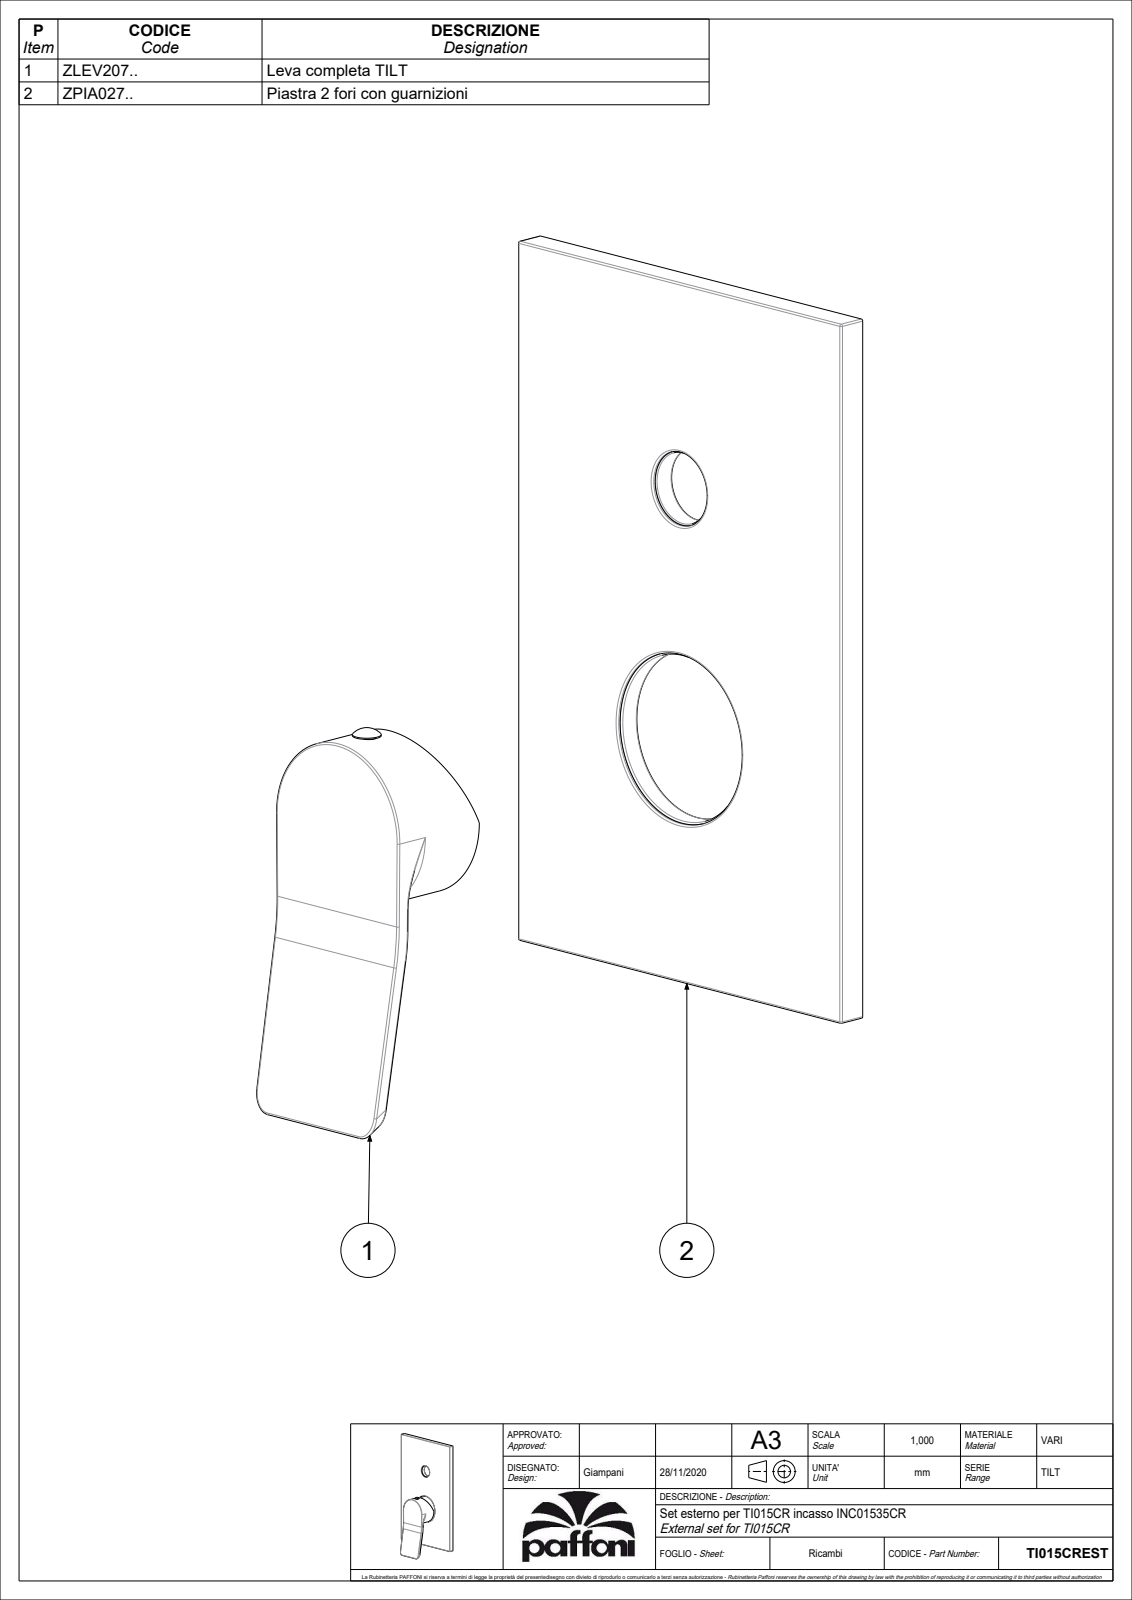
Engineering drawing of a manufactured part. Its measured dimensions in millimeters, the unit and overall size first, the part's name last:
Units: millimetres
Overall size (bounding box): 203.58 × 120 × 48.95
Round holes (diameter × count): ⌀3 ×1, ⌀19.2 ×1, ⌀20 ×1, ⌀23.2 ×1, ⌀45 ×1, ⌀46 ×1
Round bosses / shafts (diameter × count): ⌀51 ×1, ⌀49 ×1, ⌀45.5 ×1, ⌀25 ×1, ⌀23 ×1, ⌀7.6 ×1, ⌀5.5 ×1, ⌀5 ×1
Partial cylindrical surfaces — rounded edges, fillets, slot ends (radius × count): R0.5 ×18, R1 ×8, R1.5 ×2, R5 ×2, R44.14 ×1, R63 ×1
Main face-to-face distances: 7.5, 2.5, 5, 0.5, 22.5, 4.01, 39.5, 34.5, 32, 8
Hole centre spacings: 68
Volume: 140 196 mm³ · Surface area: 71 969 mm²
Bodies: 2 solids, 198 faces (71 planar, 68 cylindrical, 59 other)
Part name (STEP PRODUCT): TI015CREST
STEP written by: CREO PARAMETRIC BY PTC INC, 2020044 (CONFIG_CONTROL_DESIGN)
